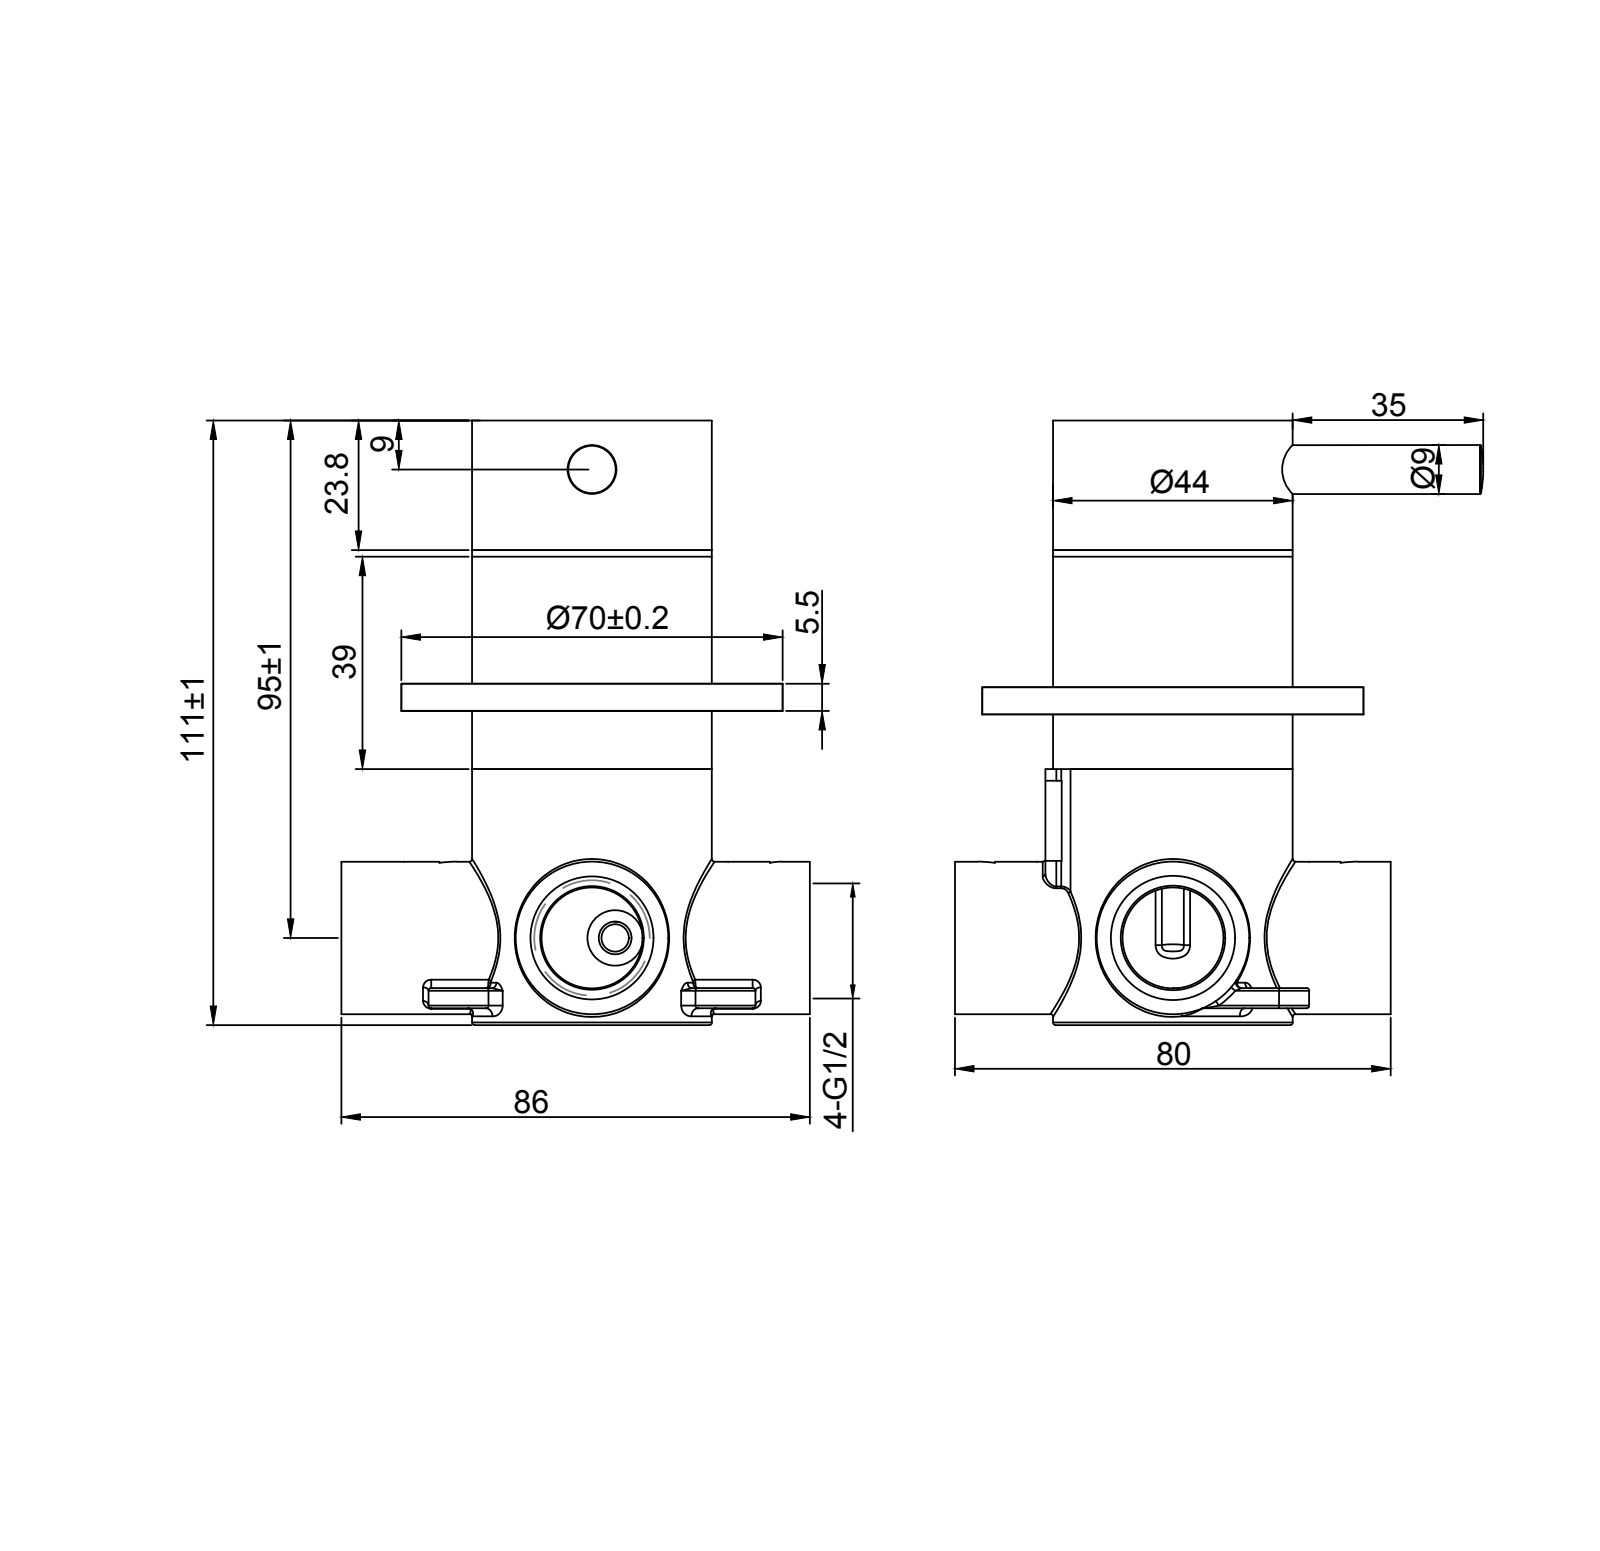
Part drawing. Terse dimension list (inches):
name: 001; WGQX4820; ZS0090501; 0014 (+4 more)
written by: CREO PARAMETRIC BY PTC INC, 2017110 (CONFIG_CONTROL_DESIGN)
unit: in
bodies: 9 solids, 571 faces (278 planar, 168 cylindrical, 125 other)
size: 4.512 × 3.622 × 3.15
volume: 11.65 in³; area: 92.07 in²
holes: 5× ⌀0.217, 5× ⌀0.276, 4× ⌀0.236, 2× ⌀0.134, 1× ⌀0.165, 1× ⌀0.394, 1× ⌀0.728, 1× ⌀1.417, 1× ⌀1.441, 1× ⌀1.462, 1× ⌀1.535, 1× ⌀1.594
bosses: 2× ⌀1.102, 2× ⌀0.189, 2× ⌀0.157, 1× ⌀2.362, 1× ⌀1.732, 1× ⌀1.575, 1× ⌀1.512, 1× ⌀1.457
rounds: 10× R0.02, 6× R0.079, 5× R0.217, 3× R0.059, 2× R0.866, 2× R1.378, 1× R0.039, 1× R0.207
face distances: 2.307, 4.512, 2.205, 1.463, 0.844, 3.048, 1.68, 0.217, 0.627, 2.832
hole spacings: 0.329, 0.374, 0.385, 0.483, 0.645, 0.354, 0.177, 0.201
